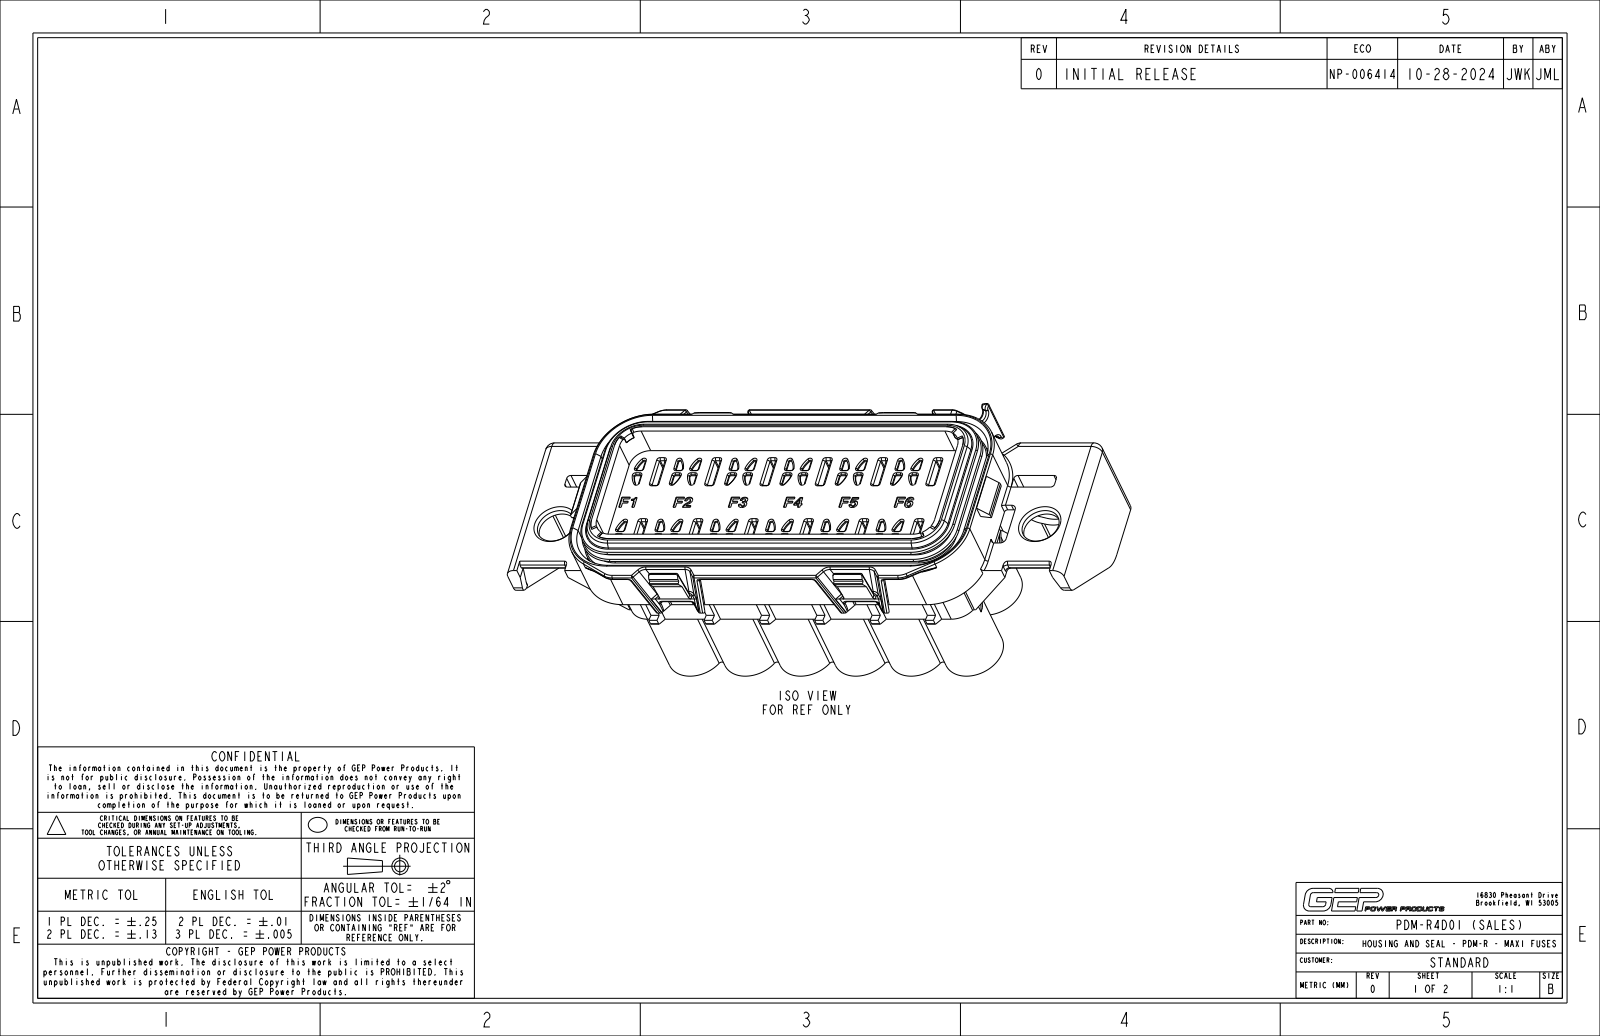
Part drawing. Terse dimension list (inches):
name: C26-1012-2D_SALES_NCF; C14-1013_INSTALLED_NCF; PDM-RS_INSTALLED_NCF_ASM; PDM-R4D01_NCF_ASM
written by: CREO PARAMETRIC BY PTC INC, 2024014 (CONFIG_CONTROL_DESIGN)
unit: in
bodies: 2 solids, 3289 faces (1685 planar, 875 cylindrical, 729 other)
size: 6.417 × 2.392 × 2.37
volume: 9.264 in³; area: 177 in²
holes: 12× ⌀0.541, 4× ⌀0.413, 2× ⌀0.492
bosses: 5× ⌀0.25, 1× ⌀0.197, 1× ⌀0.098
rounds: 157× R0.016, 148× R0.02, 64× R0.008, 46× R0.012, 46× R0.031, 39× R0.035, 26× R0.039, 16× R0.014
face distances: 0.079, 0.638, 1.516, 0.059, 0.374, 1.276, 0.453, 0.098, 1.457, 0.071
hole spacings: 0.638, 1.044, 1.276, 1.52, 0.827, 1.913, 2.084, 1.27
